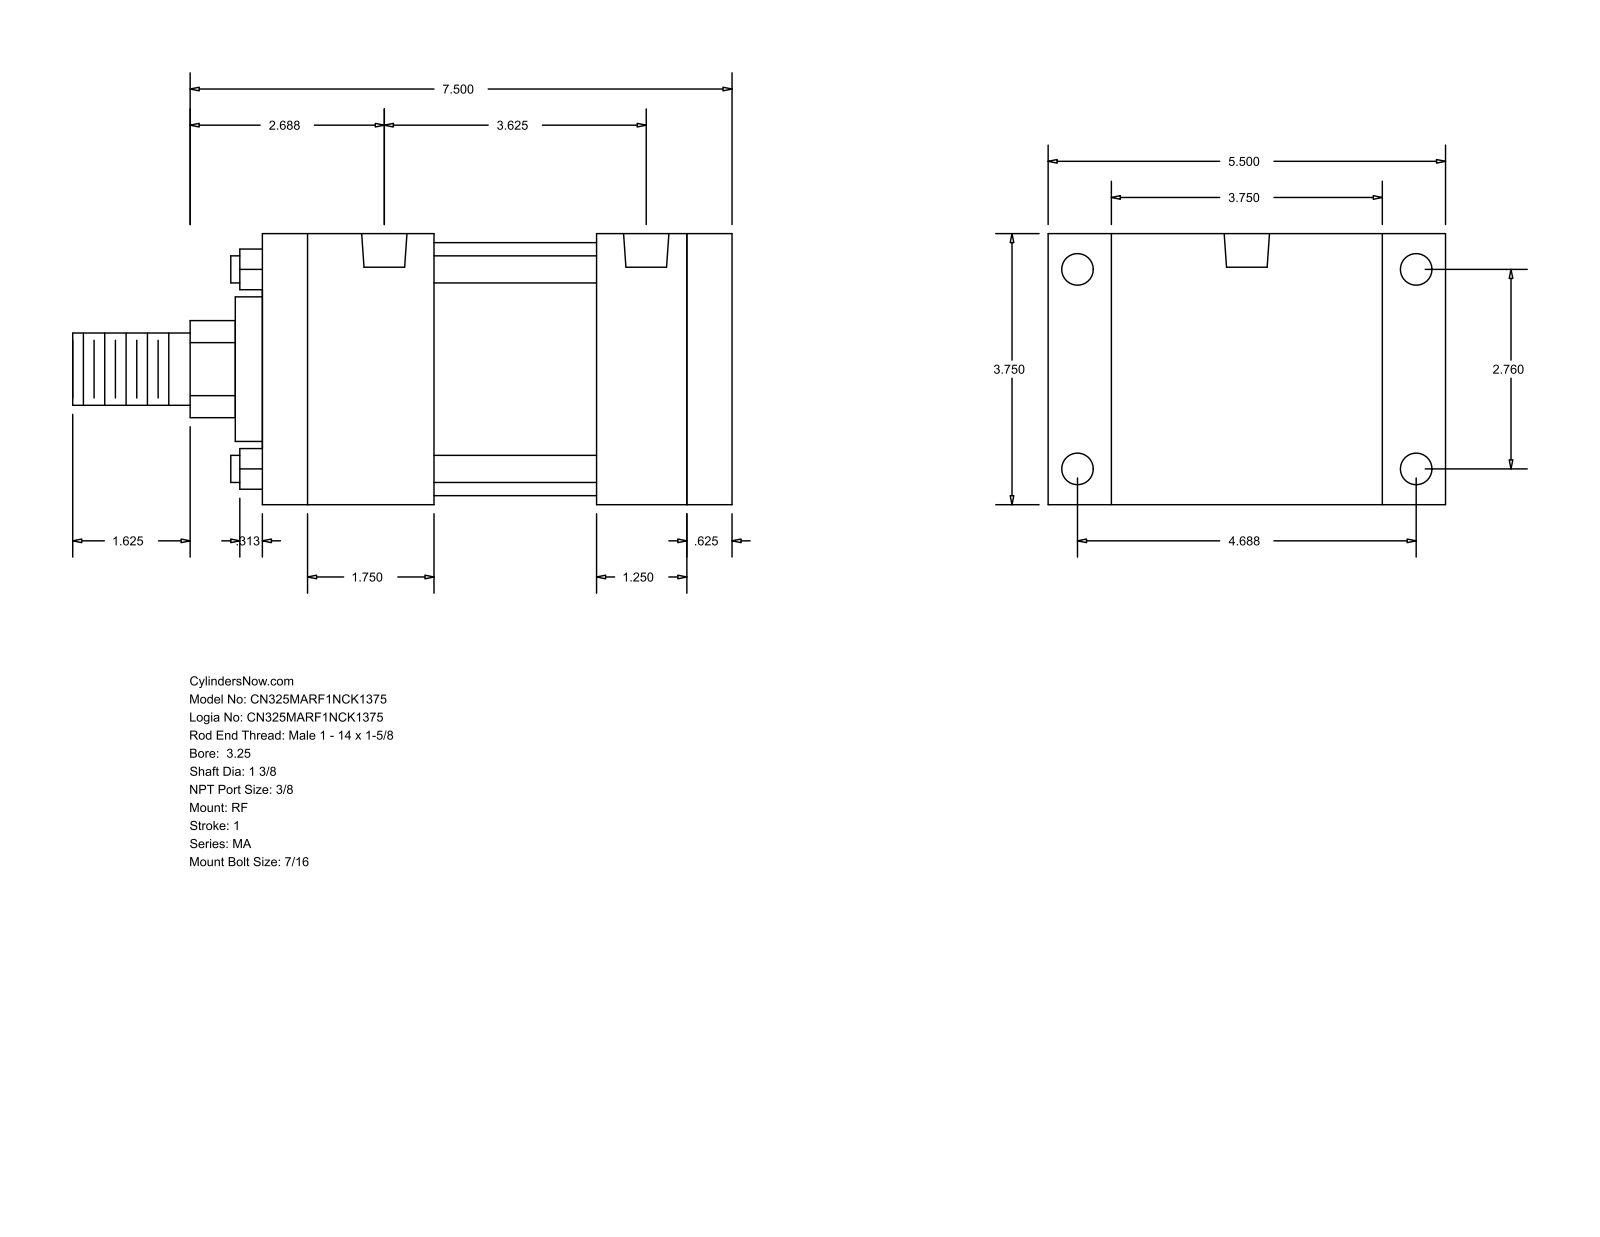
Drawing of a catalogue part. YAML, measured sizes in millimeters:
part_name: "MA_RF__0325_1.375"
step_written_by: "GSSL Pune (CONFIG_CONTROL_DESIGN)"
units: millimeters
bodies: {solids: 0, faces: 92, planar: 64, cylindrical: 28, other: 0}
overall_size: [231.78, 139.7, 95.25]
round_holes:
  - {diameter: 11.11, count: 8}
  - {diameter: 15.93, count: 2}
round_bosses_or_shafts:
  - {diameter: 9.53, count: 4}
  - {diameter: 88.9, count: 1}
  - {diameter: 50.8, count: 1}
  - {diameter: 34.92, count: 1}
  - {diameter: 25.4, count: 1}
partial_cylinders:
  - {radius: 17.06, count: 1}
face_to_face_distances: [95.24, 165.1, 15.88, 149.22, 22.23, 117.47, 117.48, 31.74, 47.62, 60.32]
hole_center_spacings: [4.77, 70.1, 82.54, 87.31, 119.06, 138.16, 92.08]
